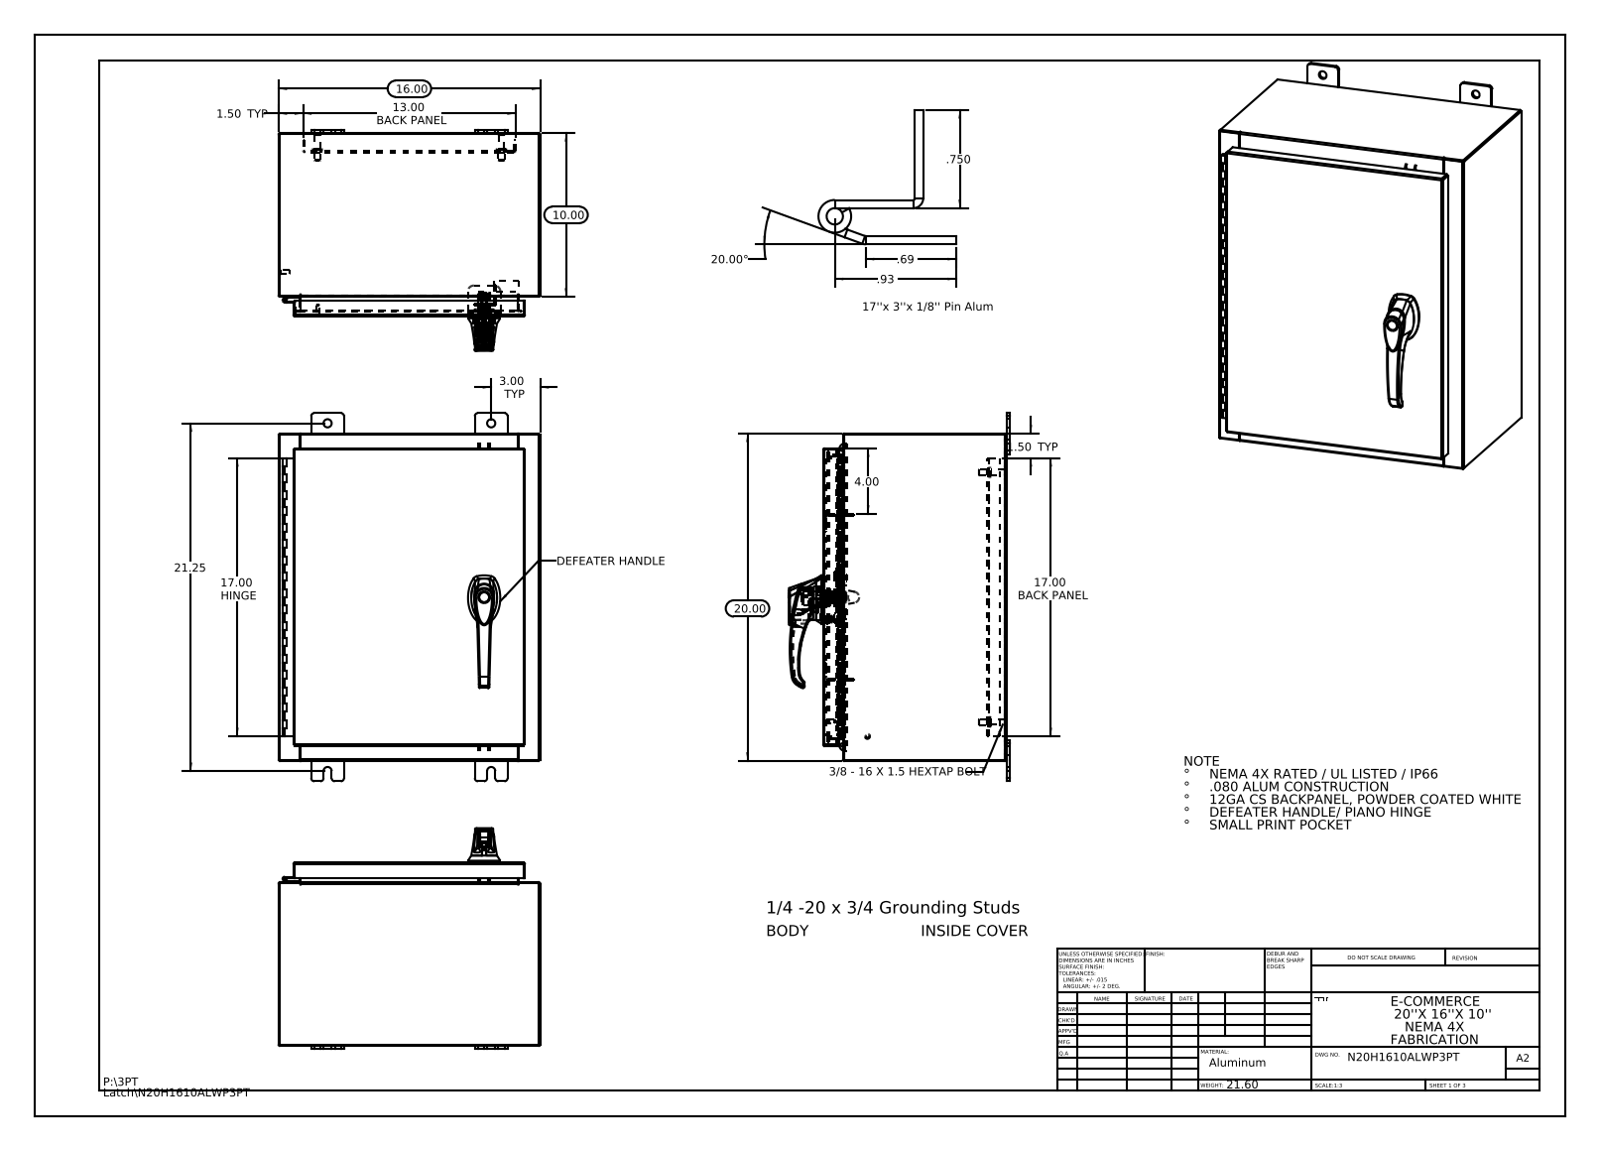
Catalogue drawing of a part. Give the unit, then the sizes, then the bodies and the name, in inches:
Units: inches
Overall size (bounding box): 22.5 × 16 × 13.495
Round holes (diameter × count): ⌀0.5 ×8, ⌀0.25 ×4, ⌀0.138 ×3, ⌀0.161 ×3, ⌀0.079 ×2, ⌀0.203 ×2, ⌀0.313 ×2, ⌀0.437 ×2, ⌀0.125 ×1, ⌀0.125 ×1, ⌀0.197 ×1, ⌀0.276 ×1
Round bosses / shafts (diameter × count): ⌀0.625 ×4, ⌀0.375 ×4, ⌀0.33 ×4, ⌀0.157 ×4, ⌀0.14 ×4, ⌀0.315 ×3, ⌀0.236 ×3, ⌀1.181 ×1
Partial cylindrical surfaces — rounded edges, fillets, slot ends (radius × count): R0.118 ×37, R0.006 ×33, R0.19 ×24, R0.013 ×22, R0.088 ×18, R0.039 ×15, R0.028 ×12, R0.008 ×6
Main face-to-face distances: 0.075, 11.126, 15.925, 19.925, 11.051, 11.201, 0.104, 1, 1.075, 10.051
Hole centre spacings: 3.404, 11.975, 0.295, 0.625, 0.841, 1.25, 1.313, 1.561
Volume: 153.2 in³ · Surface area: 3 806 in²
Bodies: 37 solids, 2402 faces (835 planar, 869 cylindrical, 698 other)
Part name (STEP PRODUCT): N20H1610ALWP3PT Cover; 00005090; N20H1610ALWP3PT Hinge Cover Side; N20H1610ALWP3PT Defeater Handle - 3 - 2500-51 ZN (+8 more)
STEP written by: SolidWorks 2013 (CONFIG_CONTROL_DESIGN)
